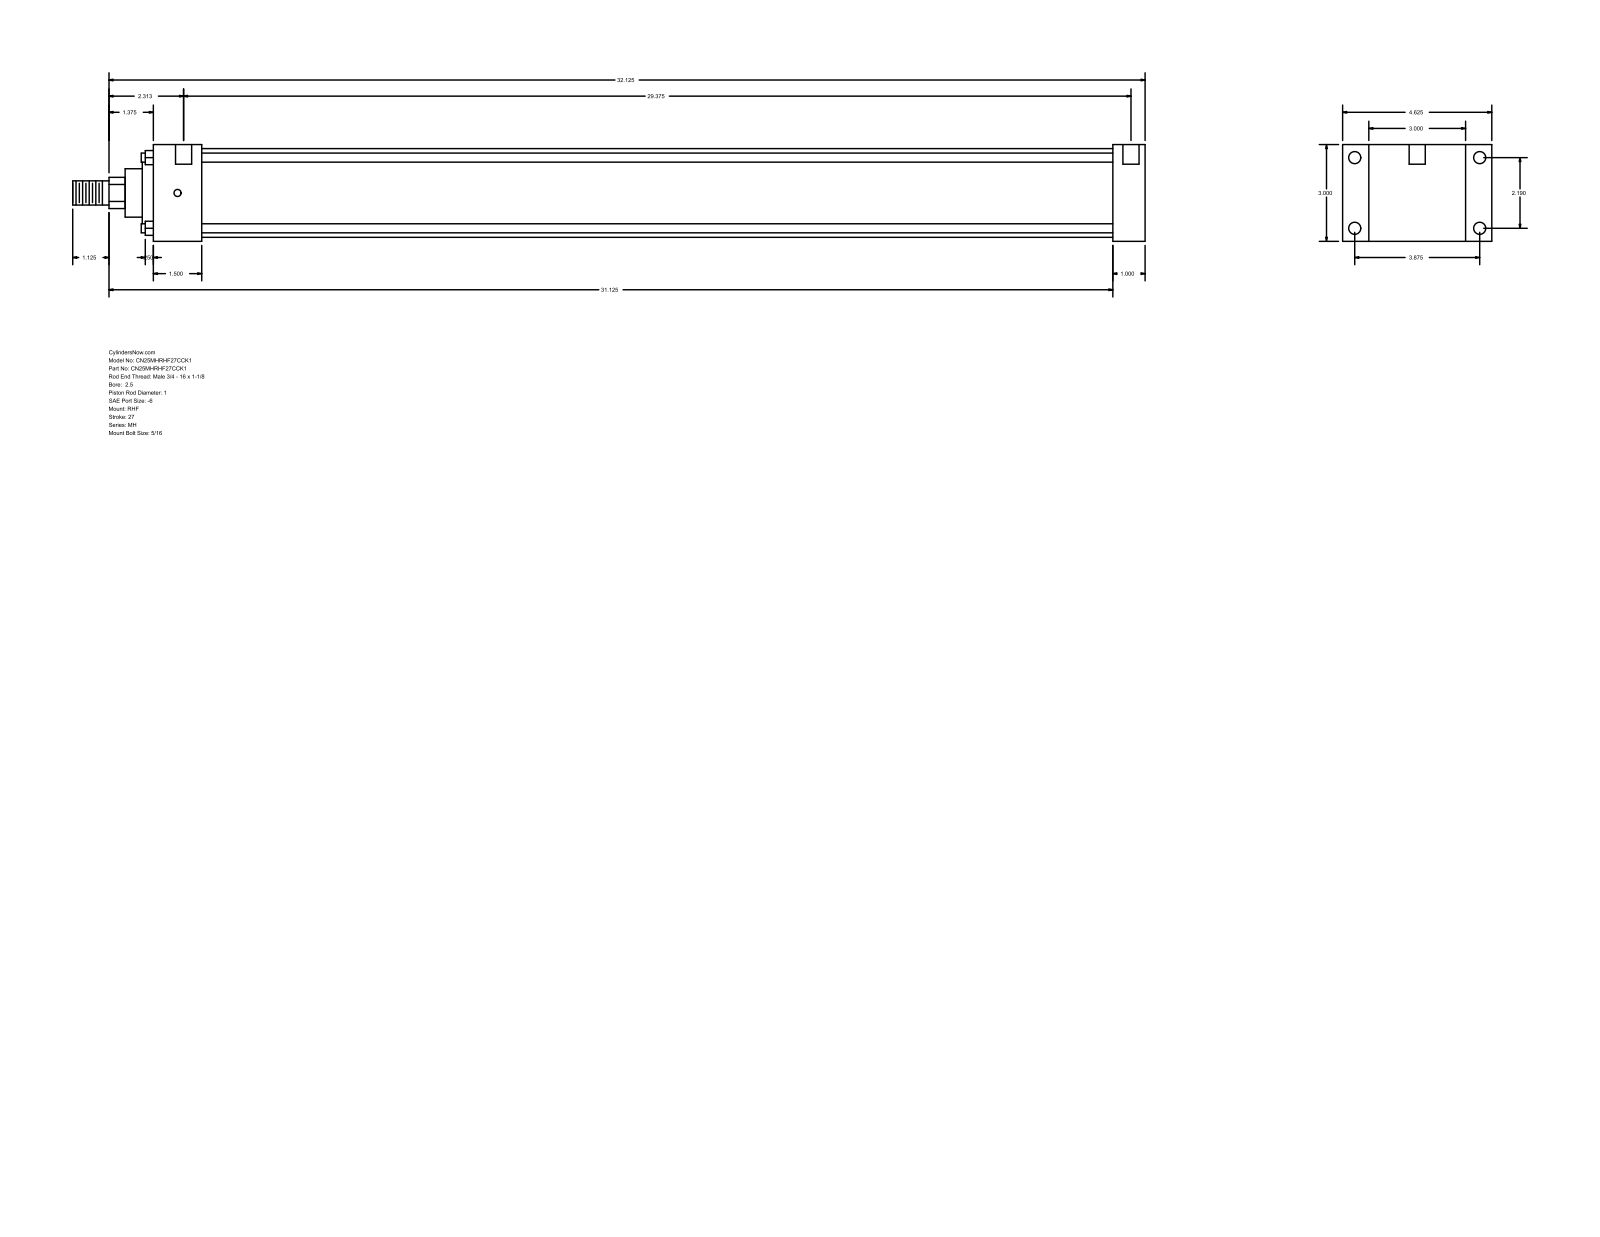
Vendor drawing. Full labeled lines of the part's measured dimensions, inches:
Part name (STEP PRODUCT): MH_RHF__0250_1
STEP written by: GSSL Pune (CONFIG_CONTROL_DESIGN)
Units: inches
Bodies: 0 solids, 90 faces (61 planar, 29 cylindrical, 0 other)
Overall size (bounding box): 33.25 × 4.625 × 3
Round holes (diameter × count): ⌀0.219 ×4, ⌀0.375 ×4, ⌀0.5 ×2
Round bosses / shafts (diameter × count): ⌀0.281 ×4, ⌀2.75 ×1, ⌀2.375 ×1, ⌀1.5 ×1, ⌀1 ×1, ⌀0.75 ×1
Partial cylindrical surfaces — rounded edges, fillets, slot ends (radius × count): R0.484 ×1
Main face-to-face distances: 3, 1, 0.813, 3.813, 29.75, 30.75, 4.625, 1.5, 28.25, 29.25
Hole centre spacings: 2.19, 3.875, 4.451, 29.687, 0.125, 0.187, 29.375, 29.5
